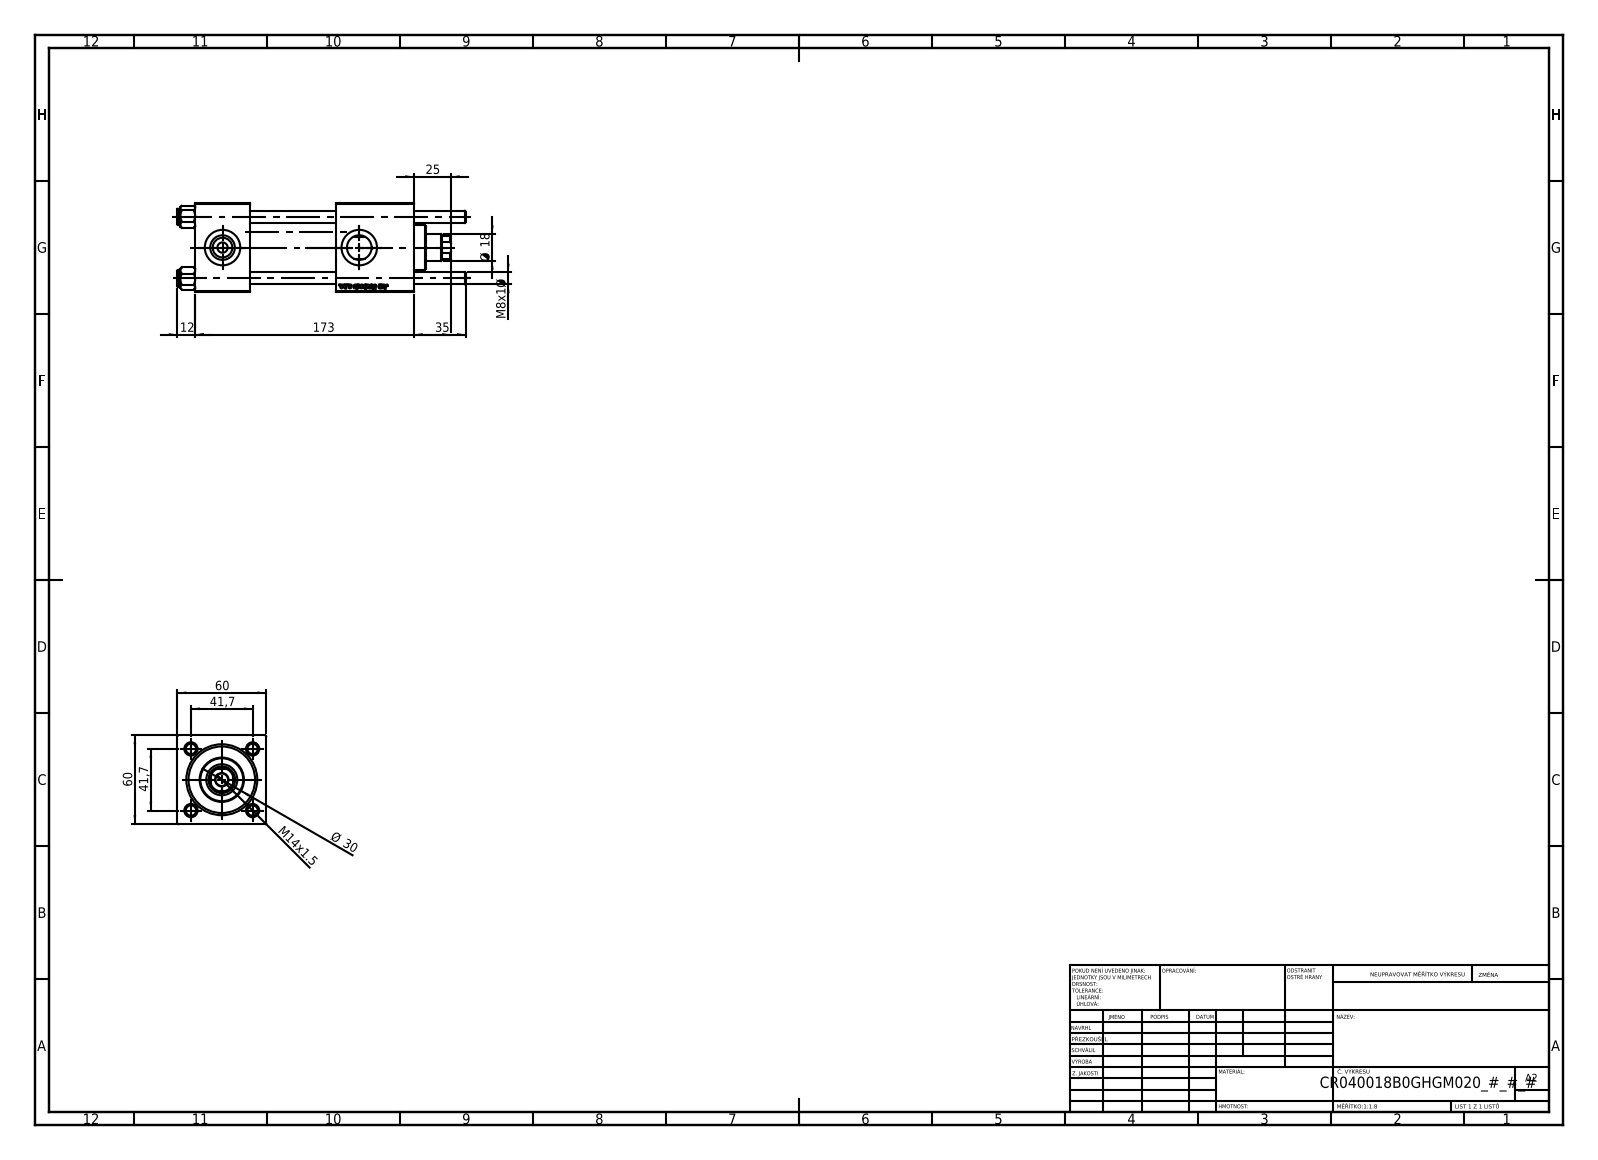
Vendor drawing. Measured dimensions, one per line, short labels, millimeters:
name: V215CR_B-1; V215CR_B_TYCINKA; NUT_M5_B; V215_VC_A (+1 more)
written by: SolidWorks 2019 (CONFIG_CONTROL_DESIGN)
unit: mm
bodies: 11 solids, 1159 faces (433 planar, 78 cylindrical, 648 other)
size: 195 × 60 × 60
volume: 413 960 mm³; area: 113 754 mm²
holes: 4× ⌀8, 2× ⌀7, 2× ⌀16.66, 2× ⌀24, 1× ⌀8.5, 1× ⌀18, 1× ⌀21, 1× ⌀31, 1× ⌀40, 1× ⌀45
bosses: 4× ⌀11, 1× ⌀46, 1× ⌀30
rounds: 1× R8.5
face distances: 60, 37, 148, 111, 58, 53, 95, 119.3, 82.3, 24.3
hole spacings: 29.49, 41.7, 58.97, 92.5
